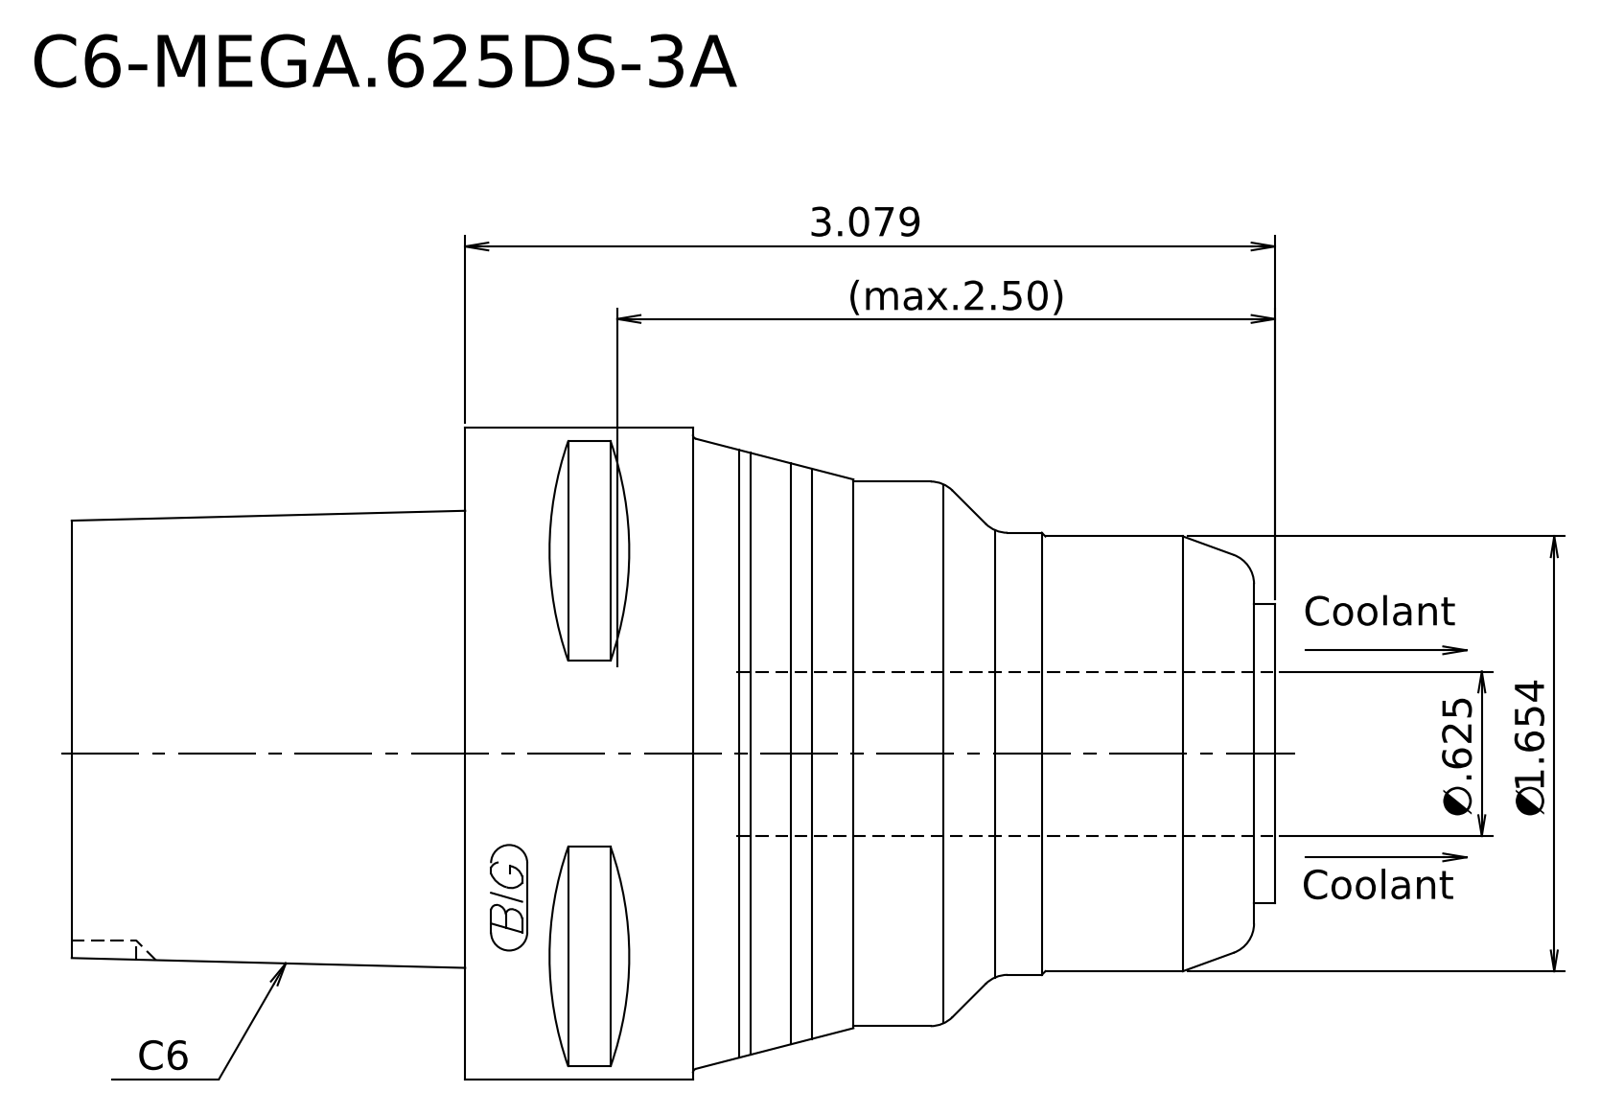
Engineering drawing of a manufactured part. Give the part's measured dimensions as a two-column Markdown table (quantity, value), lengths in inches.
| quantity | value |
| --- | --- |
| STEP written by | Kubotek KeyCreator 2011 V10.0.2 (22737) (automotive_design) |
| units | inches |
| bodies | 1 solid, 19 faces (6 planar, 5 cylindrical, 8 other) |
| overall size | 4.575 × 2.48 × 2.48 |
| volume | 13.79 in³ |
| surface area | 35.11 in² |
| round bosses / shafts (diameter × count) | 2.48 × 1, 2.071 × 1, 1.681 × 1, 1.654 × 1, 1.139 × 1 |
| main face-to-face distances | 1.496, 3.079, 4.575, 0.079, 3, 4.496, 2.213, 2.134, 0.866, 2.362 |
